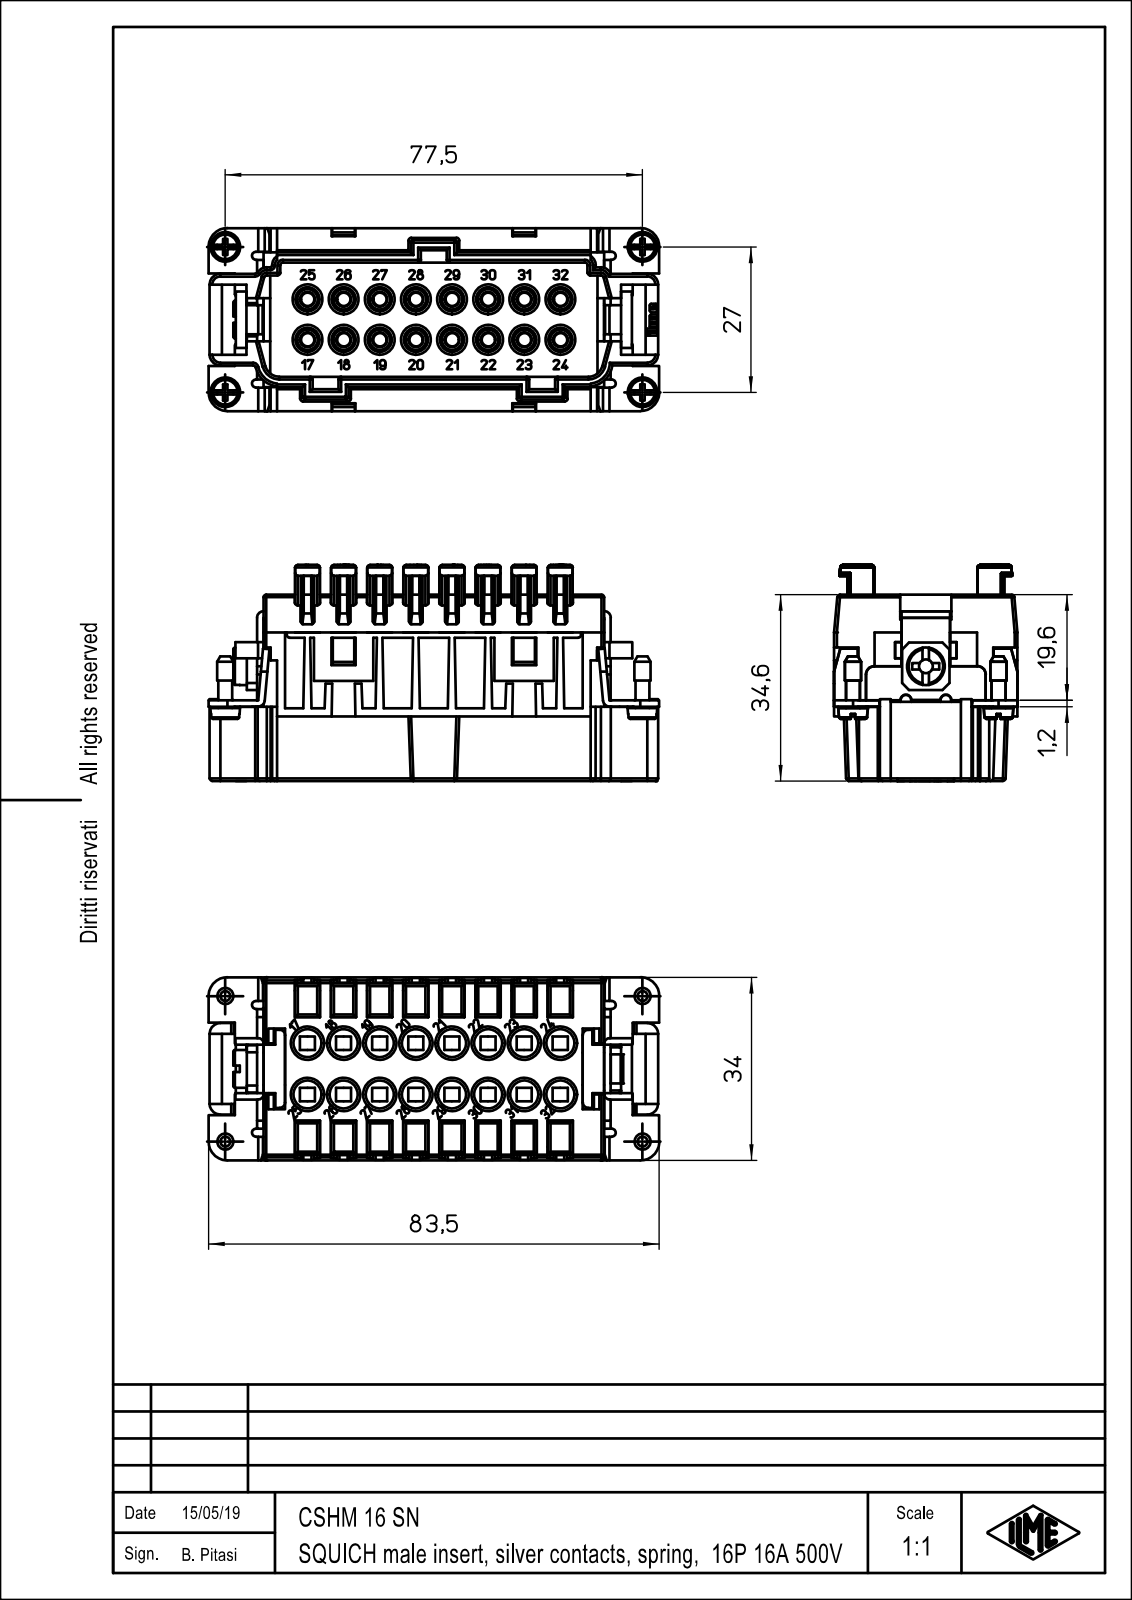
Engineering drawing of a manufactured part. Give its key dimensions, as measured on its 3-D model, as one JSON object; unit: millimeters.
{"part_name": "CSHM_16_SN", "step_written_by": "Creo Elements/Direct Modeling 20.1B 02-Apr-2019 (C) Parametric Technology GmbH (AUTOMOTIVE_DESIGN)", "units": "millimeters", "bodies": {"solids": 1, "faces": 2112, "planar": 1286, "cylindrical": 557, "other": 269}, "overall_size": [83.6, 40.1, 34], "volume_mm3": 48900, "surface_area_mm2": 30929, "round_holes": [[5.2, 16], [2.8, 4], [2.58, 1], [4.2, 1]], "round_bosses_or_shafts": [[2.48, 16], [5.5, 4], [3, 4], [2.6, 4], [7, 1], [6, 1], [4, 1]], "partial_cylinders_radius": [[0.5, 169], [0.3, 35], [1.15, 16], [1, 12], [2, 10], [1.2, 6], [0.75, 4], [3.5, 4]], "face_to_face_distances": [1.5, 26.1, 4.9, 27.6, 20.1, 6.7, 6.4, 1.2, 4, 12.5], "hole_center_spacings": [6.7, 11.62, 13.4, 16.43, 20.1, 22.23, 9.5, 26.8]}
